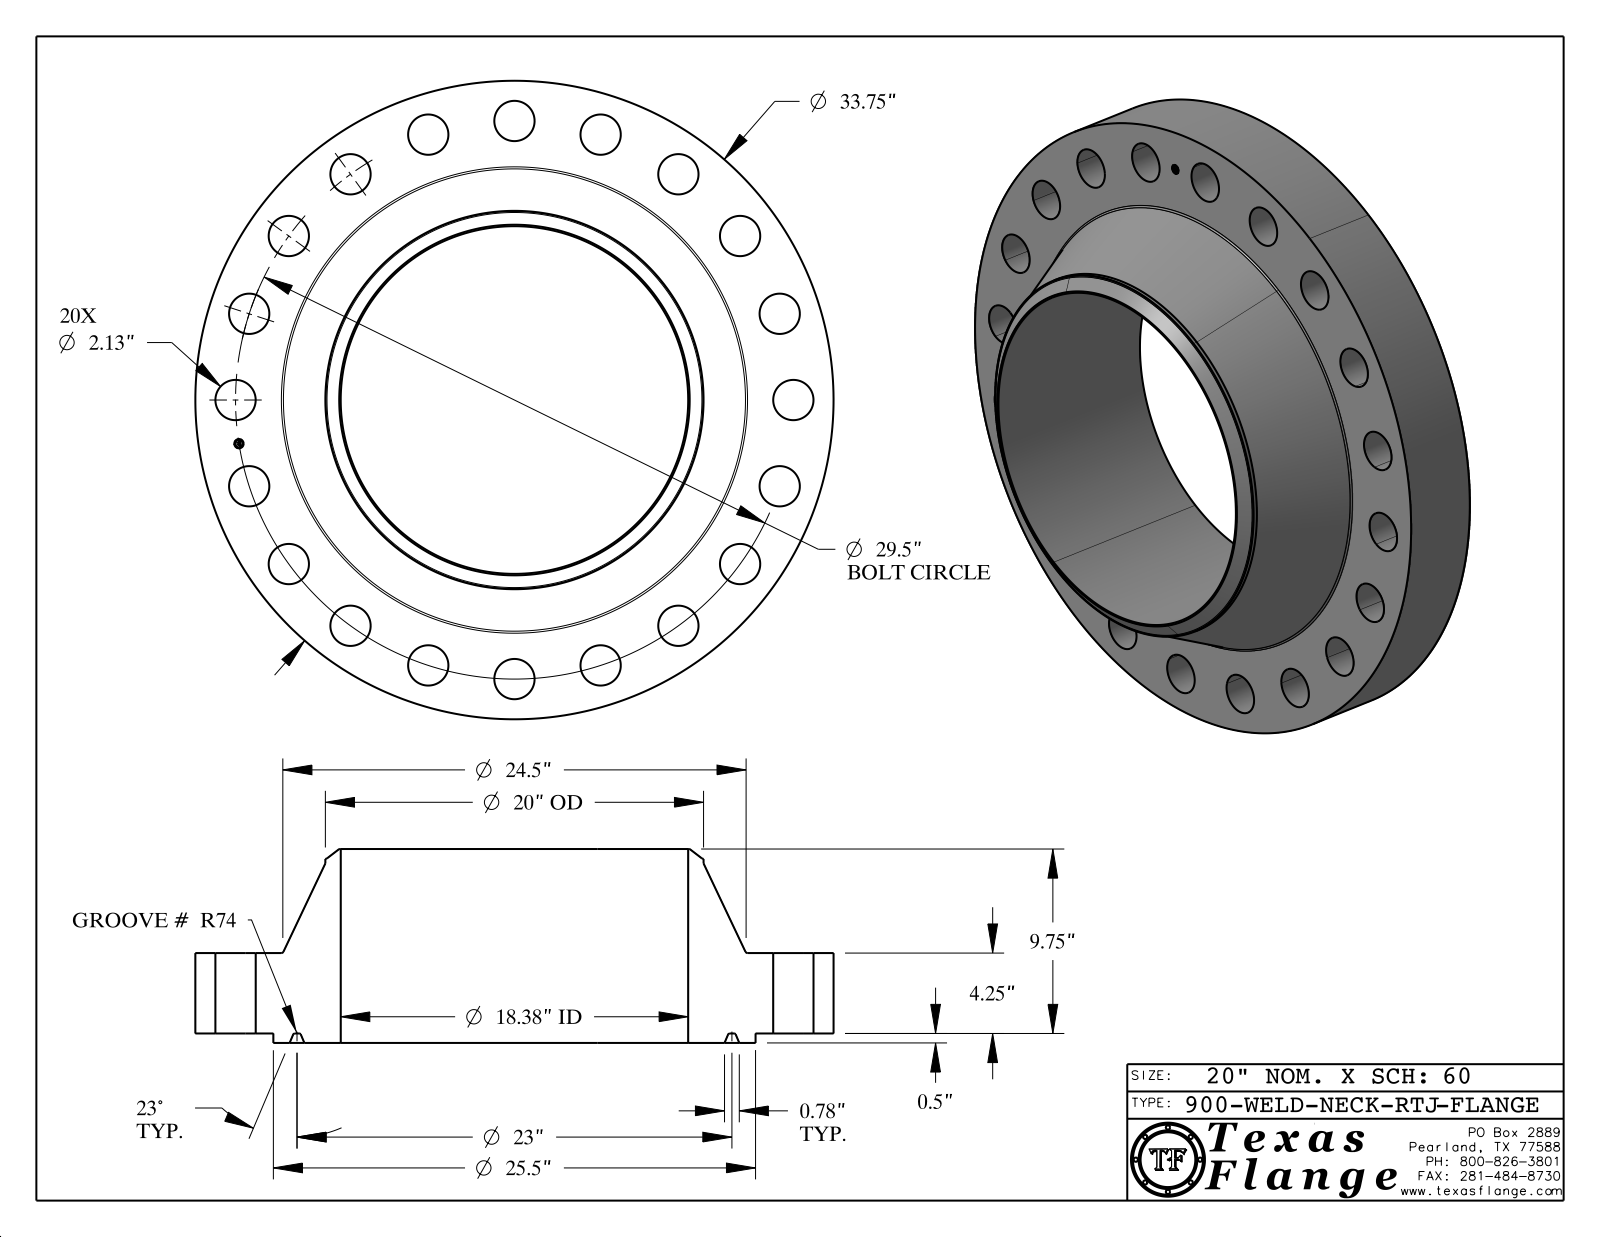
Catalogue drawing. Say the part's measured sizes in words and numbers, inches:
The part is named "900-WELD-NECK-RTJ". Its 3-D file was written by "CATIA V5 STEP AP214 (AUTOMOTIVE_DESIGN)". It is 1 solid with 457 faces: 371 planar, 68 cylindrical and 18 other. Overall it measures 33.75 by 33.75 by 10.25 inches. Its volume is 3 091 cubic inches and its surface area 3 048 square inches. Round holes: 20 of diameter 2.13, 1 of diameter 0.495, 1 of diameter 18.376. Round bosses or shafts: 8 of diameter 0.03, 1 of diameter 33.75, 1 of diameter 25.5, 1 of diameter 20, 1 of diameter 0.39. The main face-to-face distances are 4.25, 0.5, 4.75, 10.25, 9.75, 5.5, 4.735, 4.235, 0.015, 5.515. The hole center spacings are 14.75, 29.137, 4.615, 17.34, 20.859, 23.866, 26.285, 9.116.
